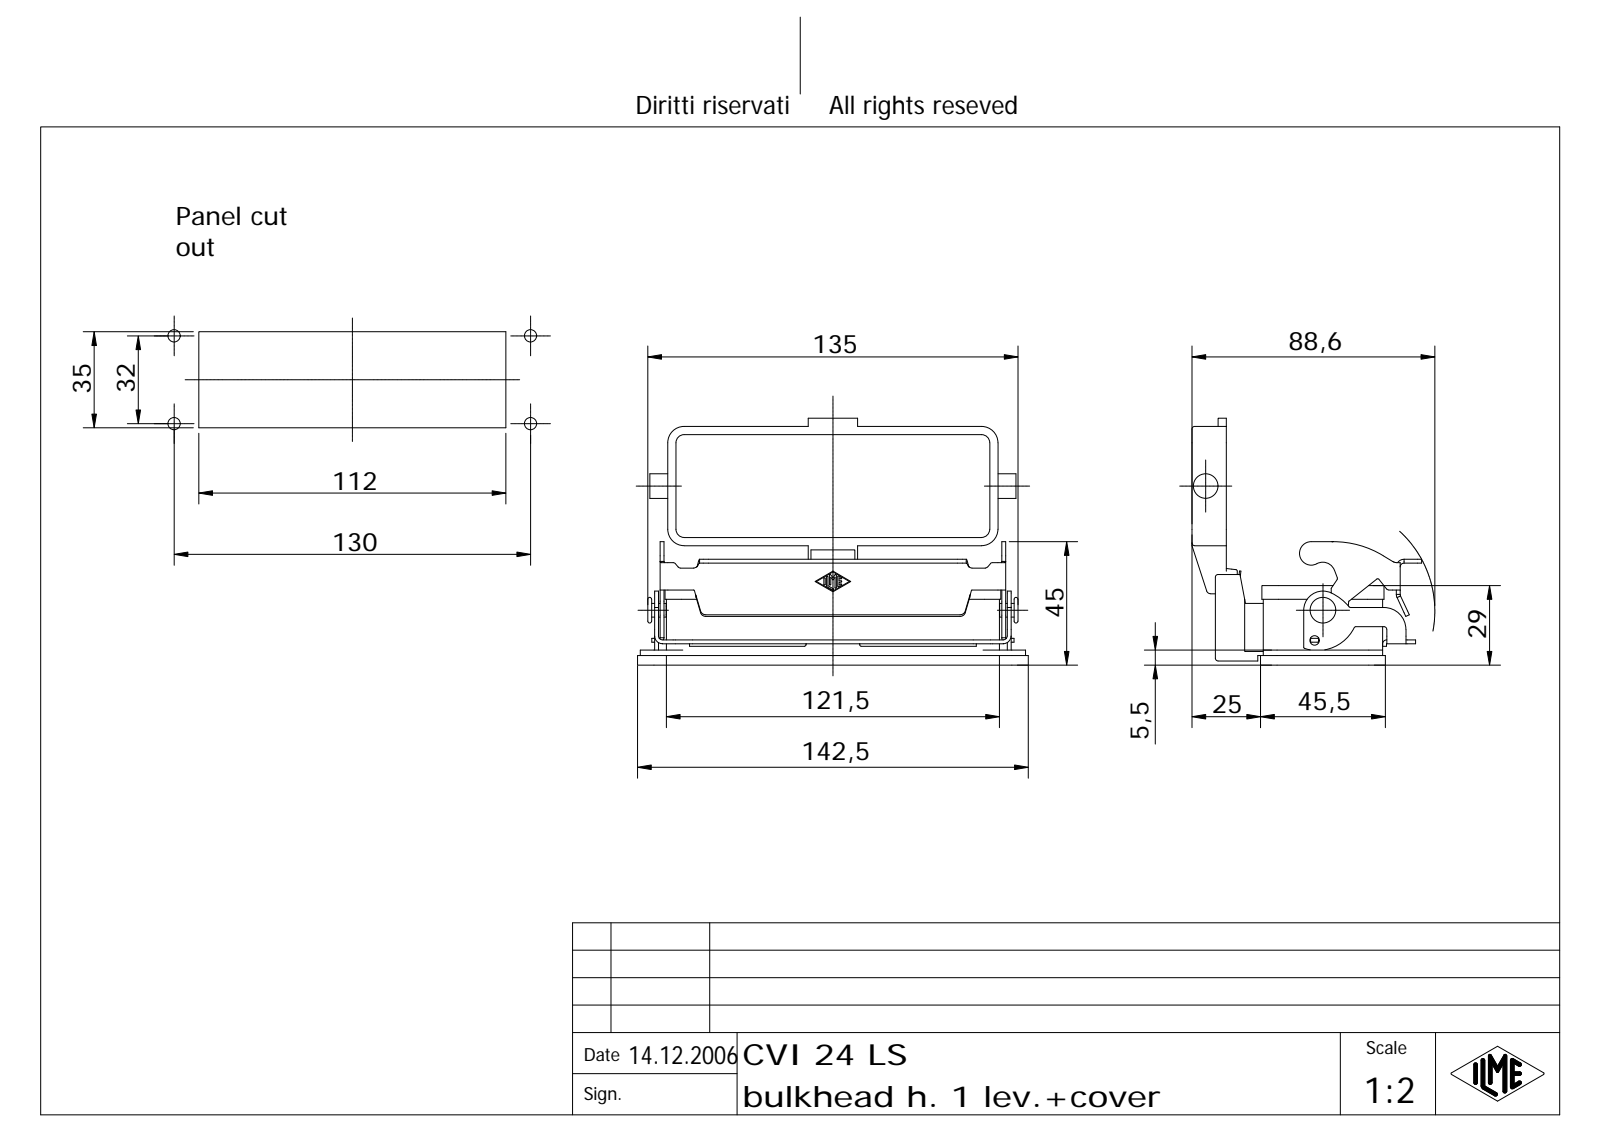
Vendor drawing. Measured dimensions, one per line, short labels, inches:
name: CVI 24 LS
written by: Autodesk Inventor 7 (AUTOMOTIVE_DESIGN)
unit: in
bodies: 4 solids, 594 faces (226 planar, 205 cylindrical, 163 other)
size: 5.61 × 3.543 × 3.296
volume: 4.831 in³; area: 98.49 in²
holes: 4× ⌀0.177, 4× ⌀0.177, 1× ⌀0.138, 1× ⌀0.157
bosses: 2× ⌀0.197, 1× ⌀0.354, 1× ⌀0.276, 1× ⌀0.126, 1× ⌀0.118
rounds: 27× R0.039, 16× R0.118, 16× R0.236, 15× R0.01, 10× R0.02, 10× R0.059, 7× R0.079, 6× R0.055
face distances: 1.594, 0.118, 0.02, 0.157, 1.713, 0.138, 0.098, 1.142, 1.476, 0.925
hole spacings: 1.26, 5.118, 5.271
